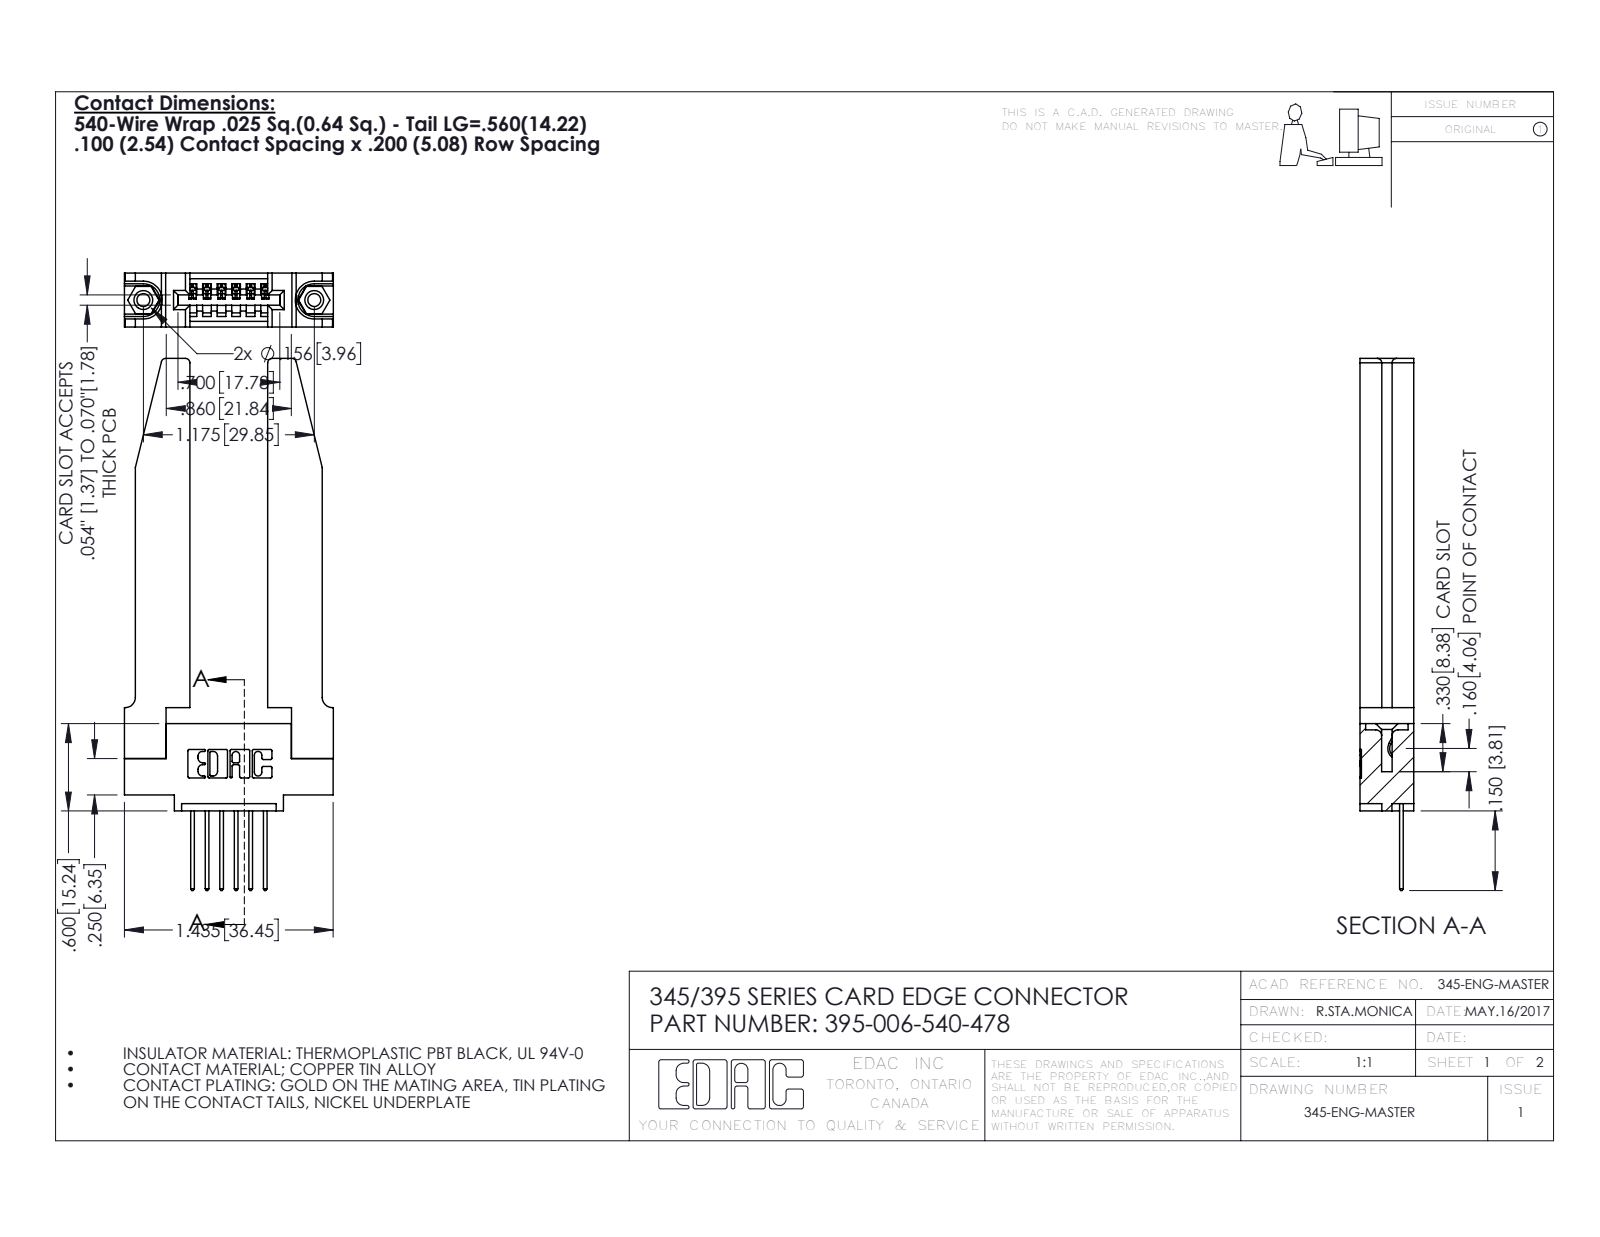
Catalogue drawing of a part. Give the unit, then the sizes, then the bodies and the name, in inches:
Units: inches
Overall size (bounding box): 3.657 × 1.436 × 0.37
Round holes (diameter × count): ⌀0.089 ×2, ⌀0.125 ×2, ⌀0.156 ×2, ⌀0.064 ×1
Round bosses / shafts (diameter × count): ⌀0.155 ×2
Partial cylindrical surfaces — rounded edges, fillets, slot ends (radius × count): R0.01 ×22, R0.006 ×12, R0.01 ×12, R0.03 ×8, R0.007 ×6, R0.031 ×6, R0.026 ×3, R0.031 ×2
Main face-to-face distances: 0.37, 0.15, 0.22, 0.535, 0.072, 0.148, 0.298, 0.077, 0.2, 0.071
Hole centre spacings: 0.27, 0.946, 1.175
Volume: 0.664 in³ · Surface area: 16.46 in²
Bodies: 11 solids, 712 faces (466 planar, 194 cylindrical, 52 other)
Part name (STEP PRODUCT): 345-220-078_345-220-078; 345-292-001_345-293-140; 395-006-540-478; 345-250-001_345-250-001-102 (+1 more)
STEP written by: SolidWorks 2016 (CONFIG_CONTROL_DESIGN)
